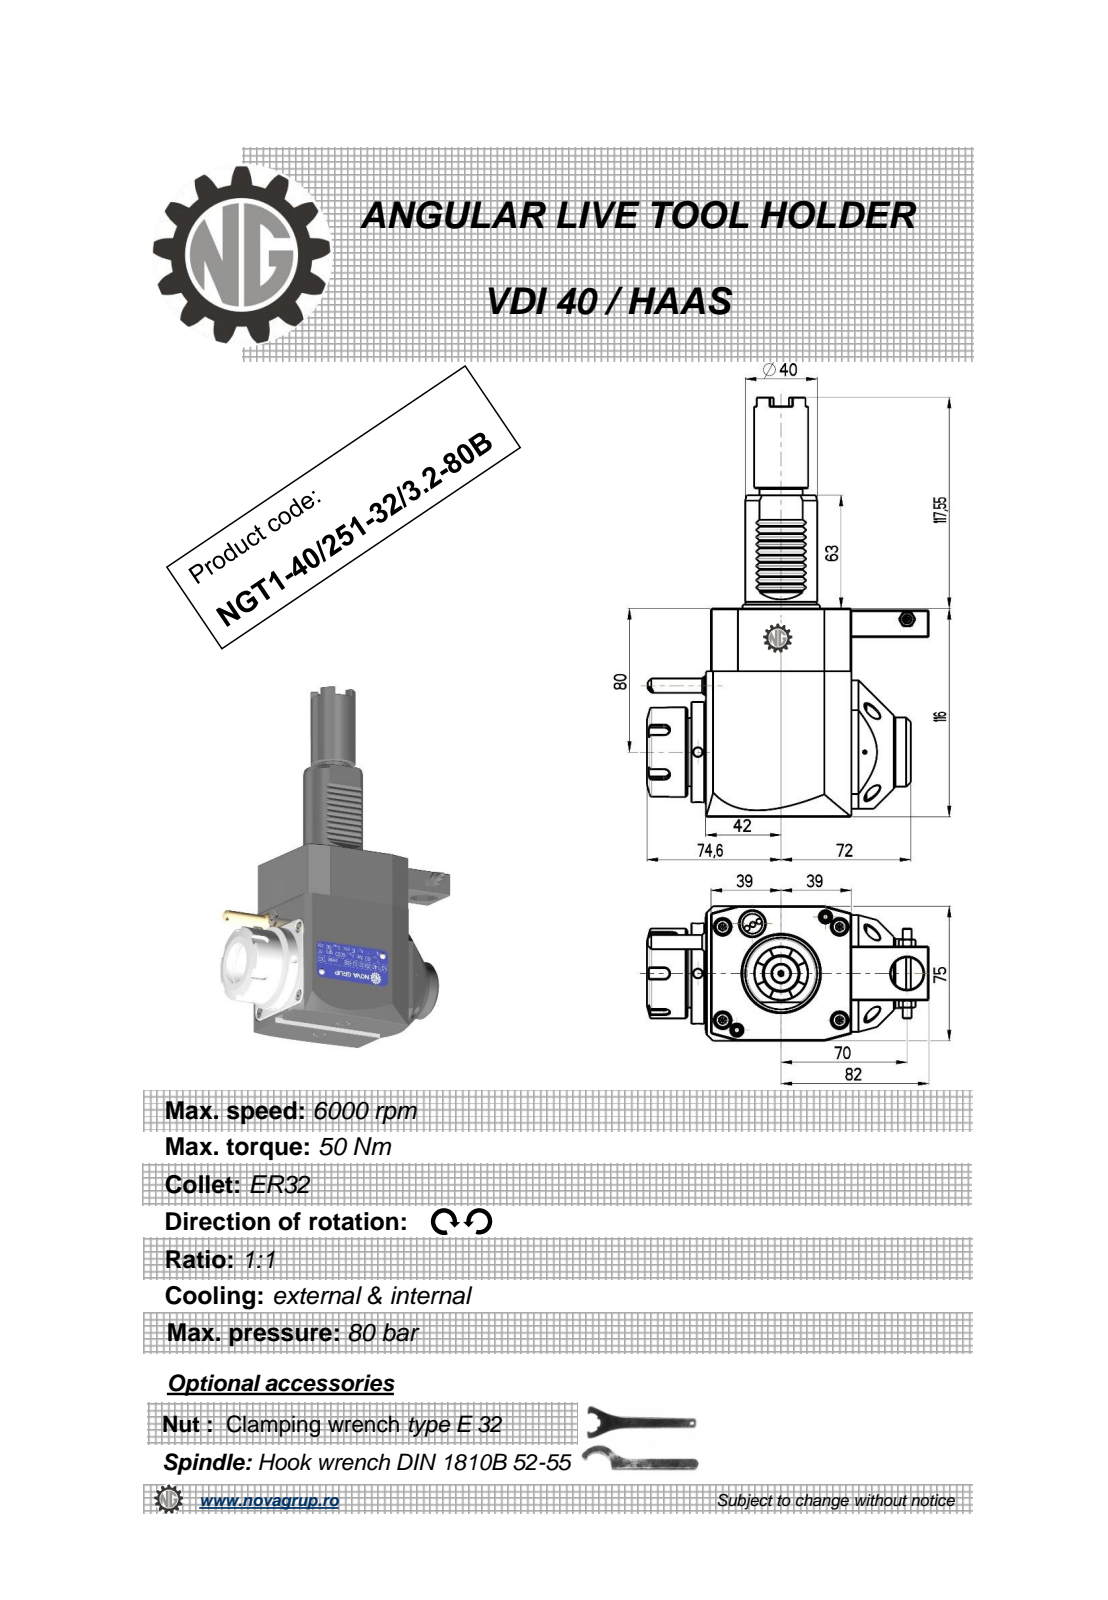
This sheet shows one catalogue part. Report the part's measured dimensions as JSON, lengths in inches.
{"part_name": "NGT1_40_251_32_3_2_80B", "step_written_by": "PRO/ENGINEER BY PARAMETRIC TECHNOLOGY CORPORATION, 2010280 (CONFIG_CONTROL_DESIGN)", "units": "inches", "bodies": {"solids": 1, "faces": 453, "planar": 216, "cylindrical": 91, "other": 146}, "overall_size": [9.195, 6.165, 2.953], "volume_in3": 58.04, "surface_area_in2": 123.5, "round_holes": [[0.197, 3], [0.118, 1], [0.165, 1], [0.374, 1], [0.709, 1], [1.063, 1]], "round_bosses_or_shafts": [[2.205, 1], [1.969, 1], [1.693, 1], [1.575, 1], [1.516, 1], [1.181, 1], [0.945, 1], [0.394, 1]], "partial_cylinders_radius": [[0.01, 12], [0.012, 10], [0.008, 6], [0.118, 5], [0.02, 1], [0.394, 1], [1.575, 1]], "face_to_face_distances": [2.953, 4.567, 3.189, 3.071, 0.118, 4.37, 0.039, 0.11, 3.181, 0.886], "hole_center_spacings": [1.558, 1.611, 2.854, 4.577, 5.425]}
